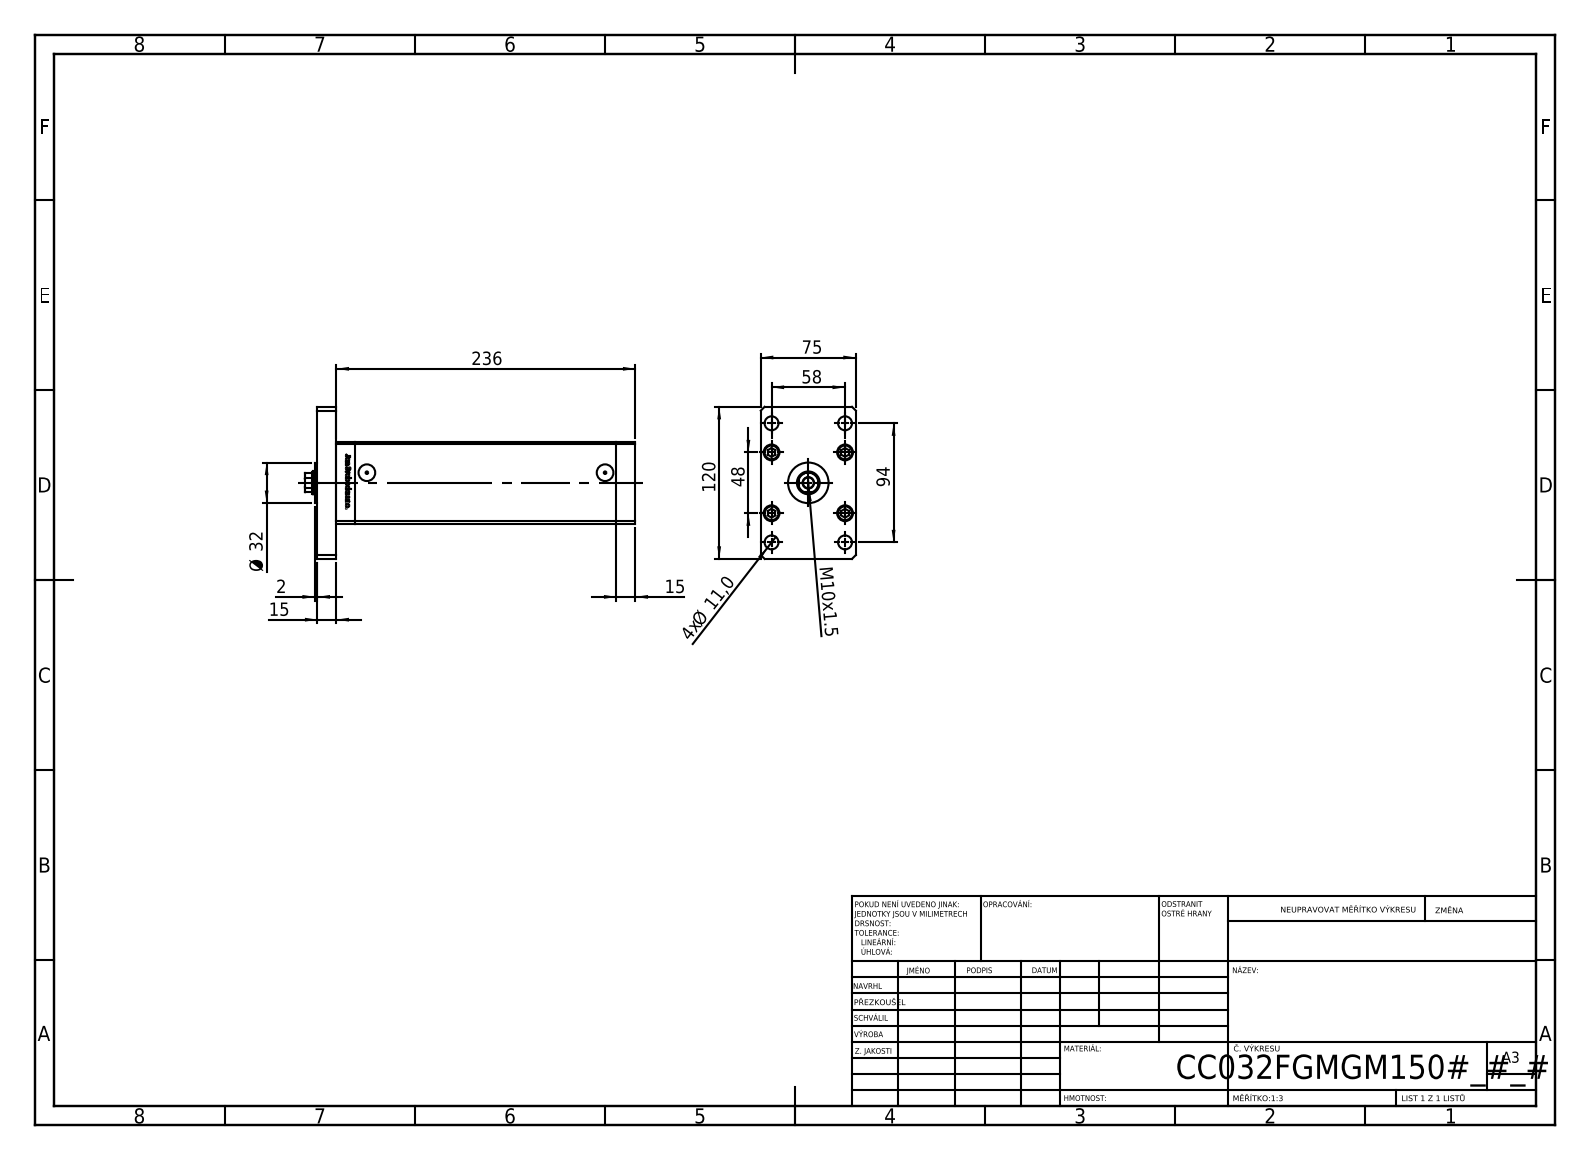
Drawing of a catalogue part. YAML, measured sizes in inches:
part_name: "V220C BACK_F; V220C_FRONT_F; V220C_VC_F; V220C_F (+2 more)"
step_written_by: "SolidWorks 2019 (CONFIG_CONTROL_DESIGN)"
units: inches
bodies: {solids: 19, faces: 1308, planar: 515, cylindrical: 187, other: 606}
overall_size: [10.276, 4.724, 2.953]
volume: 69.38
surface_area: 297.5
round_holes:
  - {diameter: 0.354, count: 5}
  - {diameter: 0.531, count: 5}
  - {diameter: 0.315, count: 4}
  - {diameter: 0.433, count: 4}
  - {diameter: 0.492, count: 4}
  - {diameter: 0.079, count: 2}
  - {diameter: 0.518, count: 2}
  - {diameter: 0.335, count: 1}
  - {diameter: 0.709, count: 1}
  - {diameter: 0.768, count: 1}
round_bosses_or_shafts:
  - {diameter: 0.492, count: 5}
  - {diameter: 0.315, count: 5}
  - {diameter: 1.26, count: 1}
partial_cylinders:
  - {radius: 0.037, count: 2}
  - {radius: 0.335, count: 1}
face_to_face_distances: [0.591, 2.953, 2.559, 8.701, 9.291, 1.181, 8.11, 9.882, 0.512, 2.146]
hole_center_spacings: [0.945, 0.906, 1.482, 2.174, 2.283, 2.456, 2.795, 3.609]
